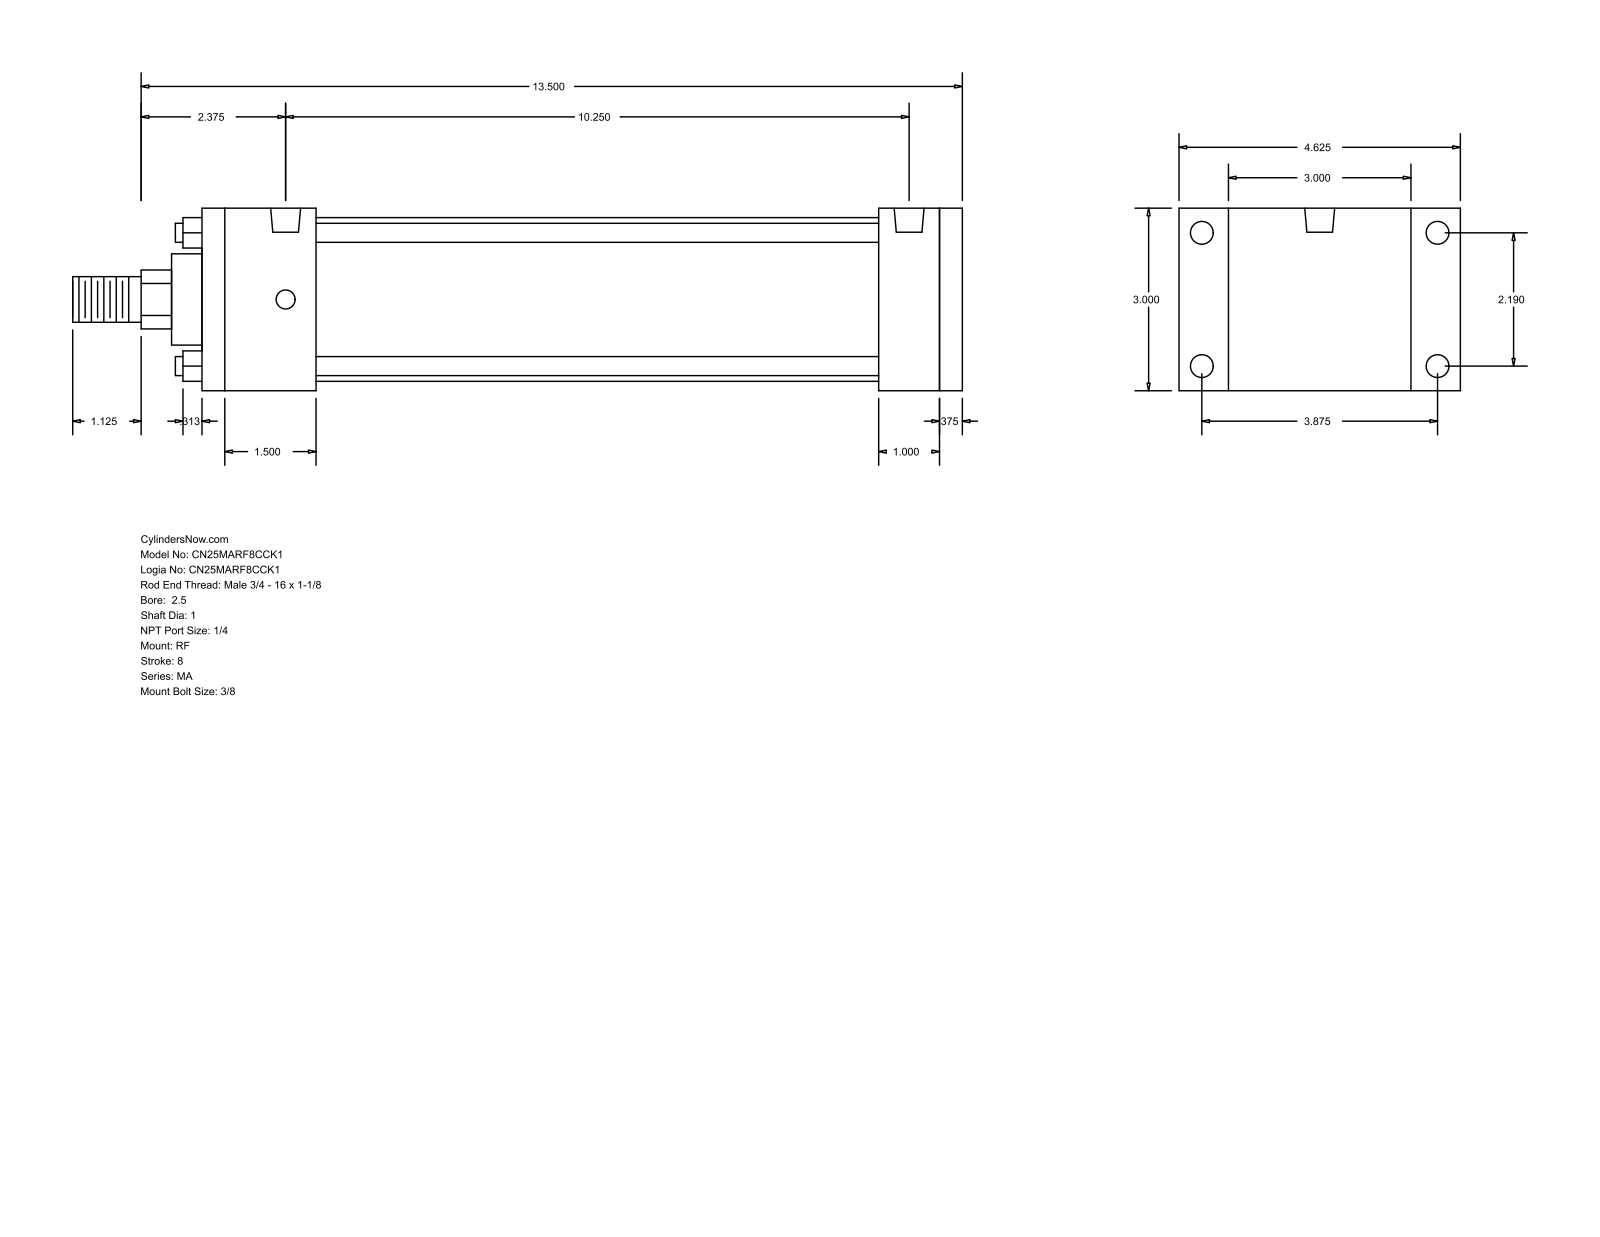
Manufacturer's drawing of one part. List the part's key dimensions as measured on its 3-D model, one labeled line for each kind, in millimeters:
Part name (STEP PRODUCT): MA_RF__0250_1
STEP written by: GSSL Pune (CONFIG_CONTROL_DESIGN)
Units: millimetres
Bodies: 0 solids, 92 faces (64 planar, 28 cylindrical, 0 other)
Overall size (bounding box): 371.48 × 117.47 × 76.2
Round holes (diameter × count): ⌀7.94 ×4, ⌀9.53 ×4, ⌀12.49 ×2
Round bosses / shafts (diameter × count): ⌀7.94 ×4, ⌀68.33 ×1, ⌀38.1 ×1, ⌀25.4 ×1, ⌀19.05 ×1
Partial cylindrical surfaces — rounded edges, fillets, slot ends (radius × count): R12.29 ×1
Main face-to-face distances: 76.2, 317.5, 307.98, 9.52, 25.4, 47.63, 282.58, 234.95, 260.35, 269.87
Hole centre spacings: 55.62, 98.42, 113.05, 260.35
